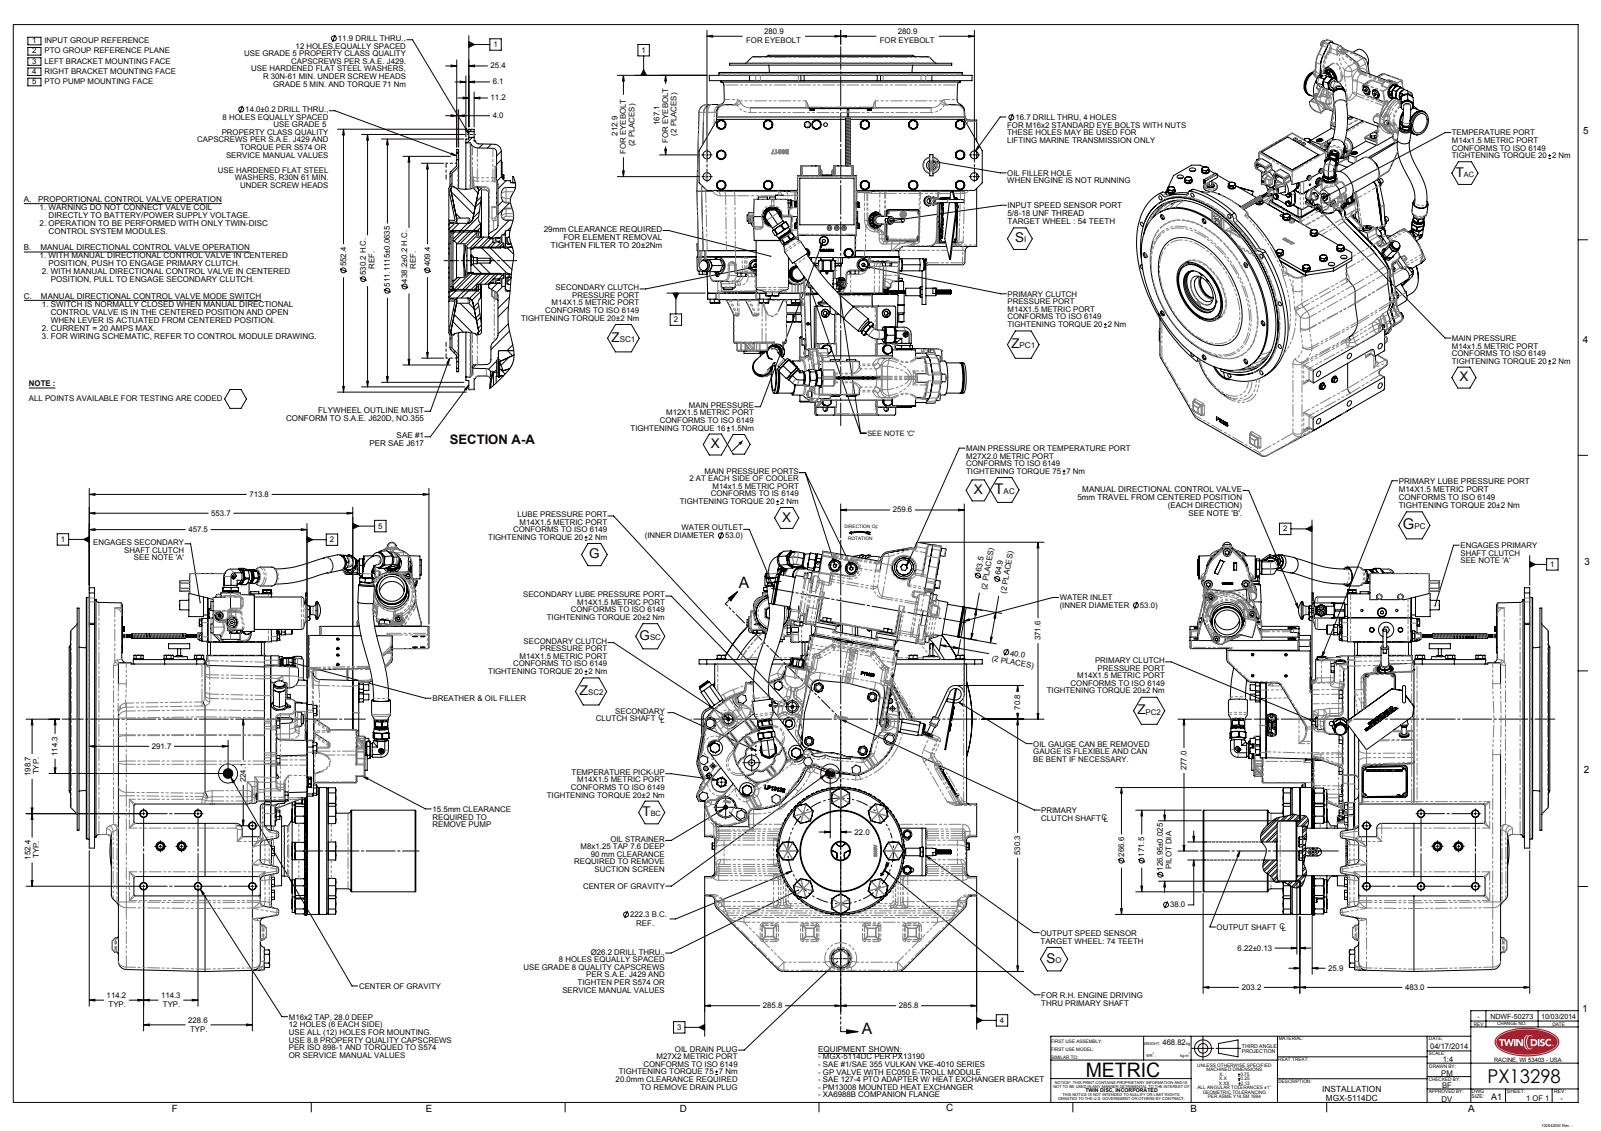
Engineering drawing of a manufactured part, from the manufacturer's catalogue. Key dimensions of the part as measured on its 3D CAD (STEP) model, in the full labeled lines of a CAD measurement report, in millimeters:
Part name (STEP PRODUCT): PX13298
STEP written by: SolidWorks 2010 (AUTOMOTIVE_DESIGN)
Units: millimetres
Bodies: 0 solids, 5613 faces (1841 planar, 1765 cylindrical, 2007 other)
Overall size (bounding box): 901.9 × 755.9 × 599.6
Round holes (diameter × count): ⌀11.9 ×12, ⌀14 ×8, ⌀10 ×7, ⌀25 ×7, ⌀16 ×6, ⌀16.7 ×4, ⌀5 ×3, ⌀40 ×3, ⌀4.8 ×2, ⌀8 ×2, ⌀8.8 ×2, ⌀9.3 ×2
Round bosses / shafts (diameter × count): ⌀19.8 ×18, ⌀19 ×14, ⌀36.4 ×8, ⌀13 ×8, ⌀19.1 ×7, ⌀37.7 ×5, ⌀12 ×5, ⌀32 ×4
Partial cylindrical surfaces — rounded edges, fillets, slot ends (radius × count): R2 ×94, R5 ×72, R45.9 ×68, R1 ×67, R4 ×67, R10 ×65, R1.5 ×58, R3 ×46
Main face-to-face distances: 320.2, 9.3, 22, 298.2, 8.5, 13.5, 306.7, 0.4, 13.1, 21.6
Hole centre spacings: 265.1, 137.2, 265.1, 374.9, 459.2, 512.1, 111.1, 137.2
